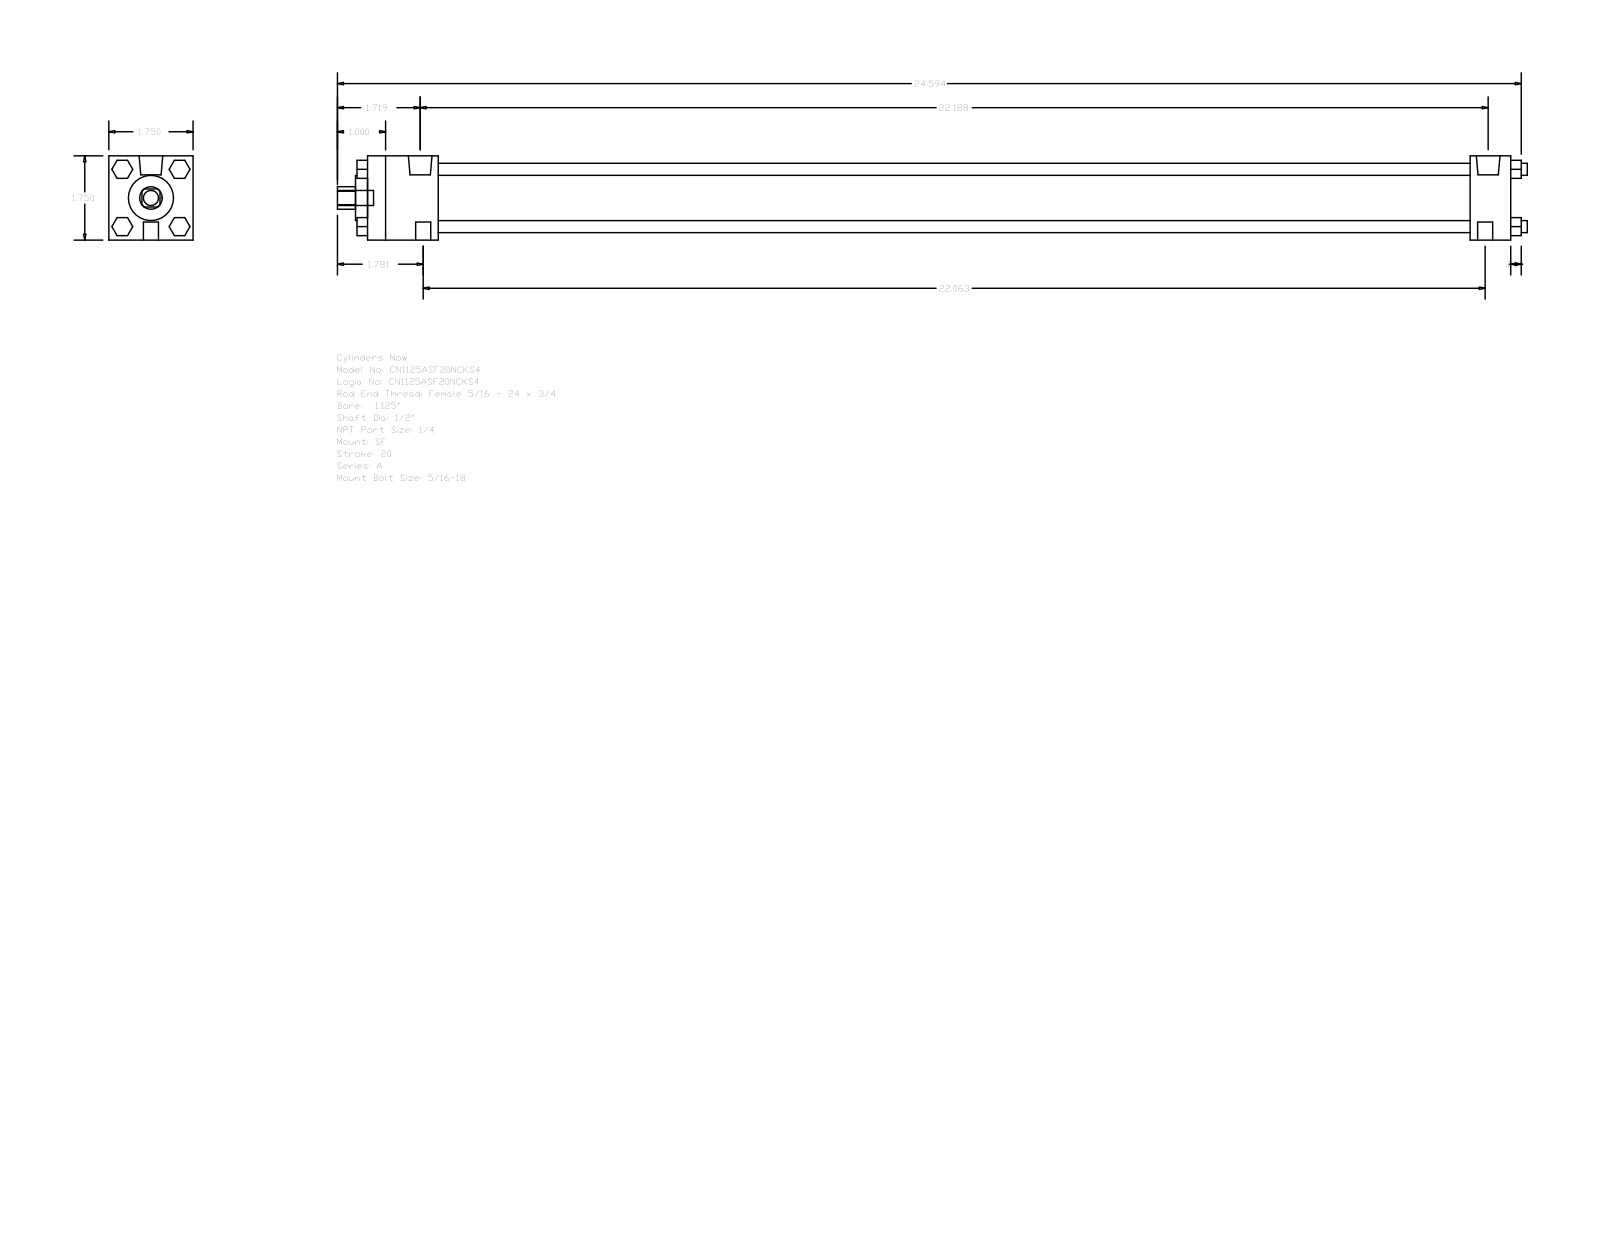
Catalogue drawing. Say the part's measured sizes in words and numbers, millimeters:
The part is named "A_SF__0112_0.5". Its 3-D file was written by "GSSL Pune (CONFIG_CONTROL_DESIGN)". It is 0 solids with 120 faces: 92 planar, 28 cylindrical and 0 other. Overall it measures 627.86 by 44.45 by 44.45 millimeters. Round holes: 1 of diameter 12.7, 1 of diameter 23.81, 1 of diameter 31.88. Round bosses or shafts: 4 of diameter 6.35, 3 of diameter 7.94, 2 of diameter 12.49, 2 of diameter 5.56. Partial cylindrical surfaces (rounded edges, fillets, slot ends): 1 of radius 5.94. The main face-to-face distances are 44.46, 603.24, 581.81, 21.43, 37.3, 544.51, 565.94, 9.53, 5.59, 9.52.
